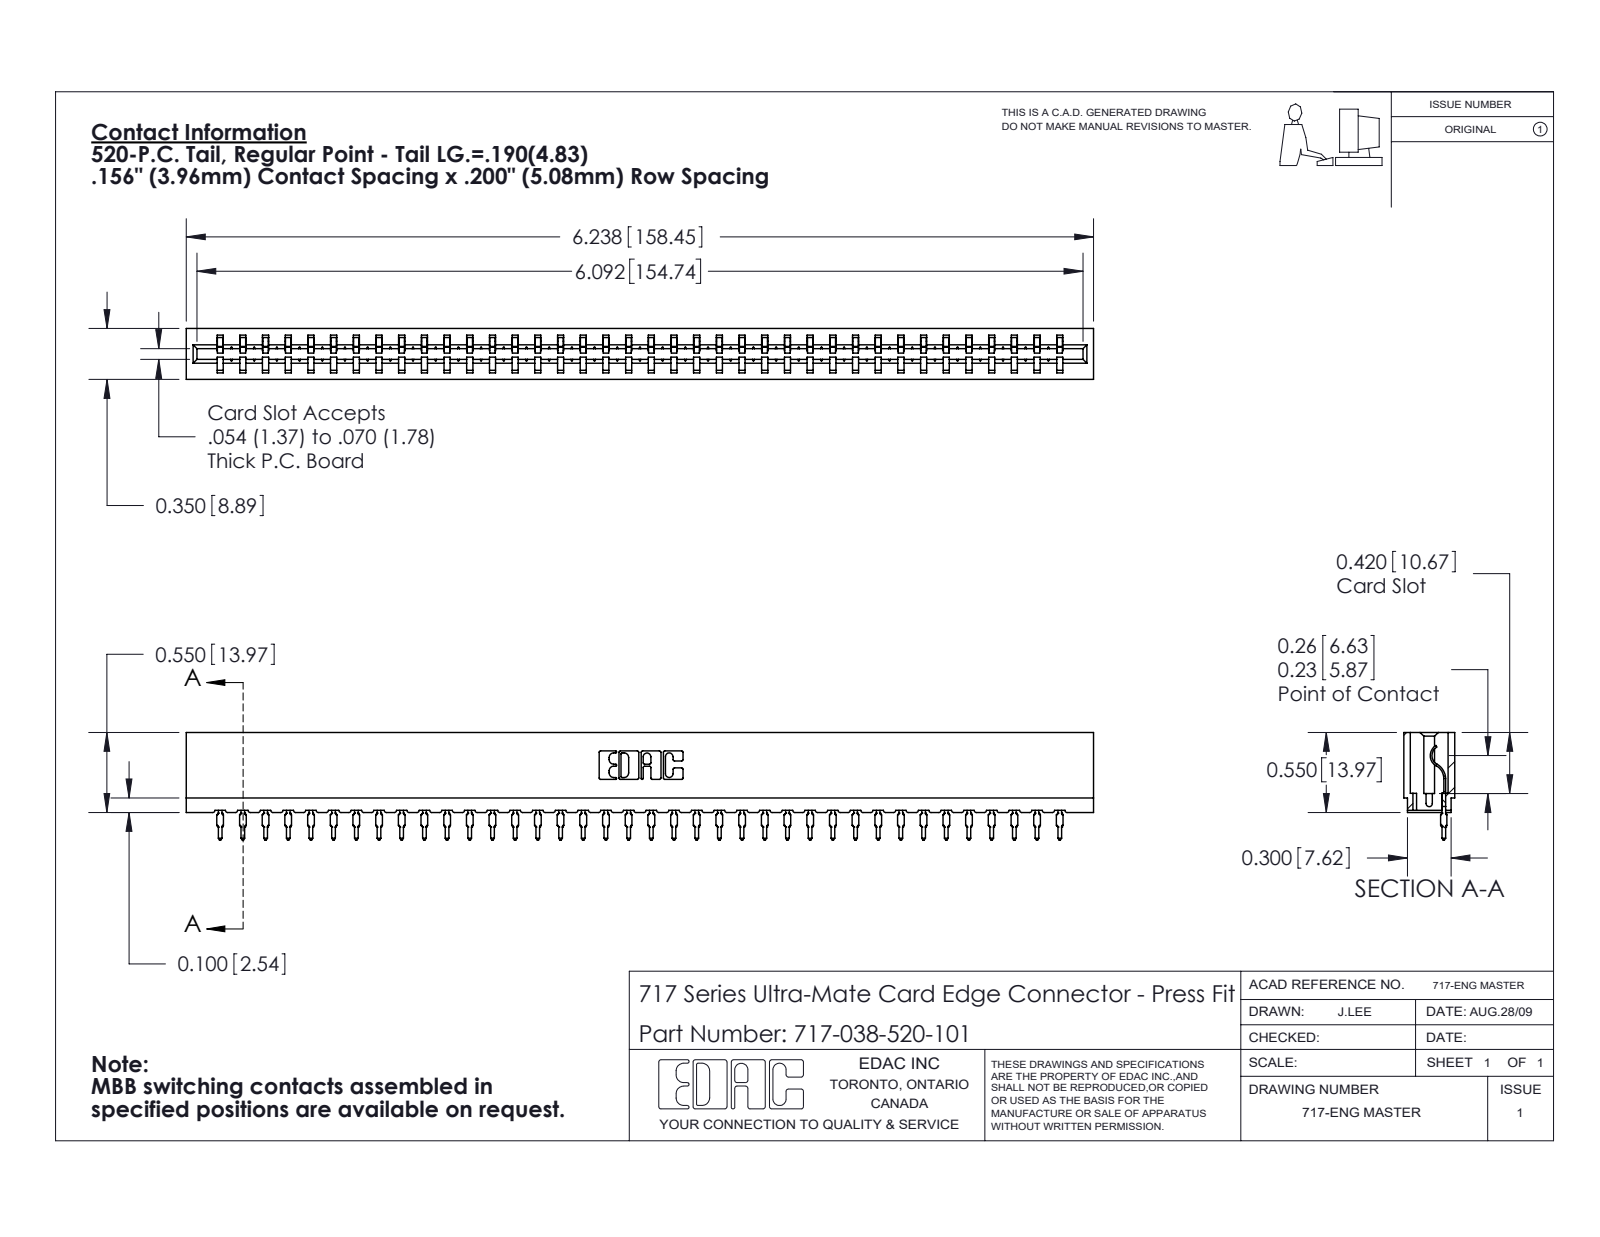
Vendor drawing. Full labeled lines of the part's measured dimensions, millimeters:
Part name (STEP PRODUCT): 717 Part_Insulator Option - 06; 717-038-520-101; 745-292-001_520
STEP written by: SolidWorks 2020 (CONFIG_CONTROL_DESIGN)
Units: millimetres
Bodies: 39 solids, 4388 faces (2638 planar, 762 cylindrical, 988 other)
Overall size (bounding box): 158.4 × 18.8 × 8.9
Volume: 13 300 mm³ · Surface area: 18 430 mm²
Partial cylindrical surfaces — rounded edges, fillets, slot ends (radius × count): R0.4 ×76, R0.5 ×76, R0.3 ×22, R0.2 ×6, R0.8 ×6, R0.1 ×4, R0.3 ×4, R0.7 ×3
Main face-to-face distances: 5.4, 3.5, 8.9, 1.9, 1.1, 7.7, 2.4, 4.2, 0.6, 8.3
